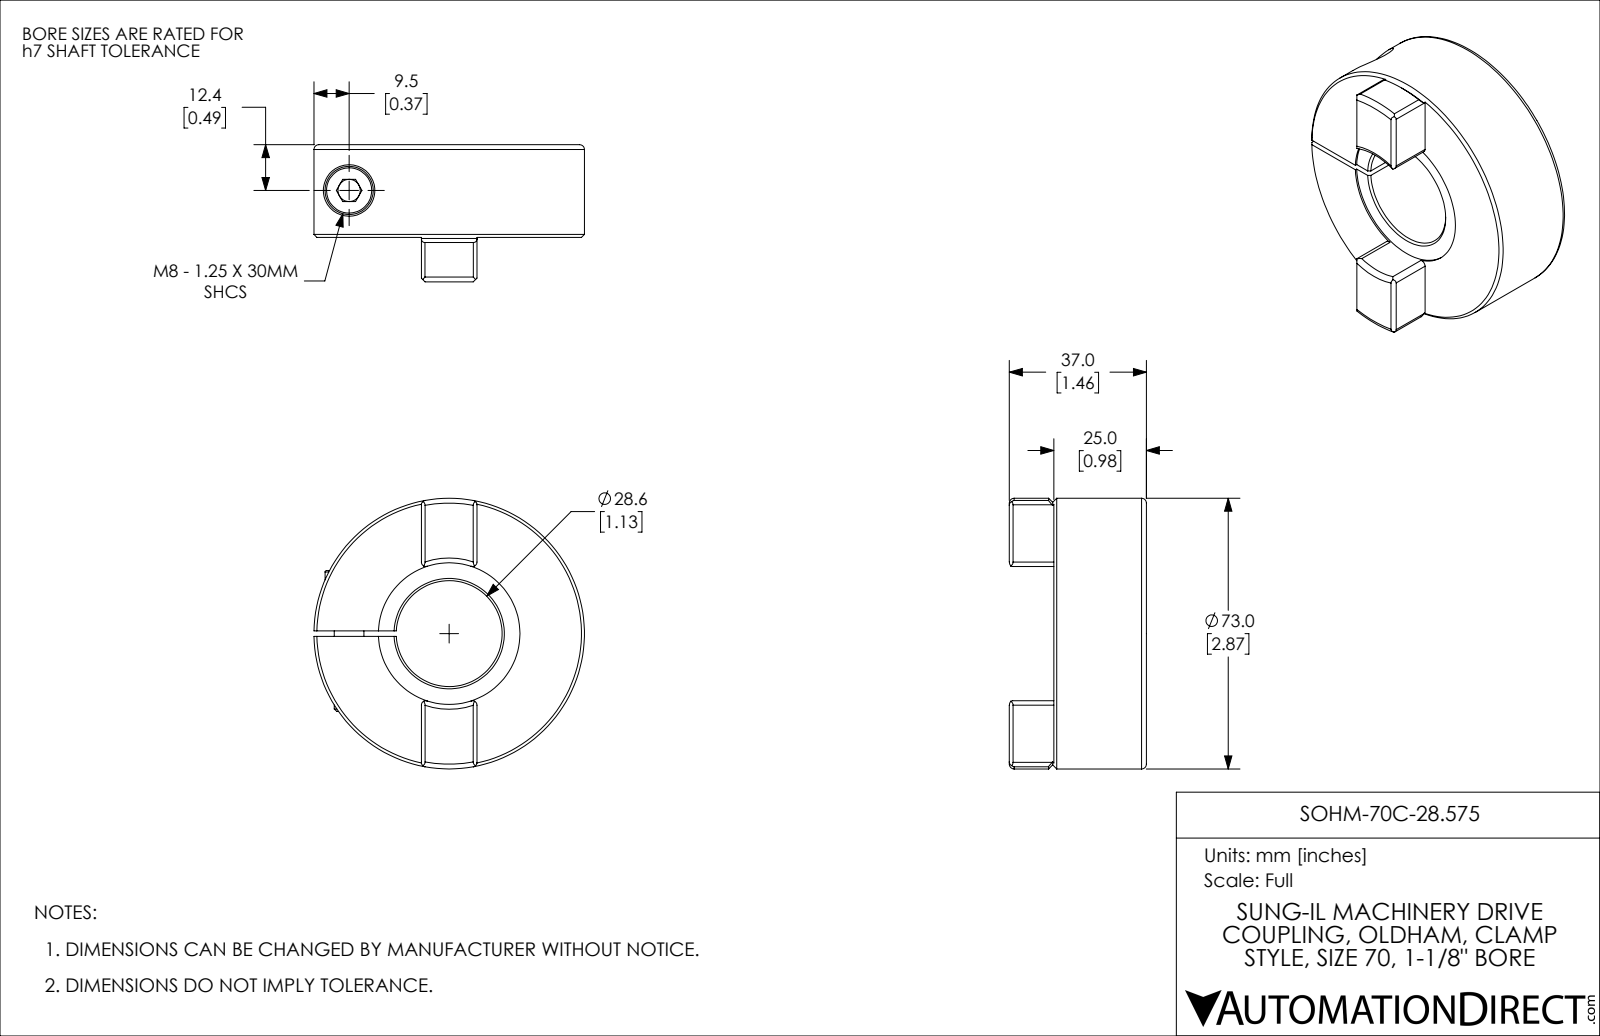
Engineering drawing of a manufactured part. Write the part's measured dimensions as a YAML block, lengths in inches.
part_name: "SOHM-70C-28.575"
step_written_by: "SolidWorks 2021 (CONFIG_CONTROL_DESIGN)"
units: inches
bodies: {solids: 2, faces: 94, planar: 35, cylindrical: 30, other: 29}
overall_size: [2.874, 2.874, 1.457]
volume: 5.63
surface_area: 30.74
round_holes:
  - {diameter: 0.236, count: 1}
  - {diameter: 0.268, count: 1}
  - {diameter: 0.335, count: 1}
  - {diameter: 0.547, count: 1}
  - {diameter: 1.125, count: 1}
  - {diameter: 1.504, count: 1}
round_bosses_or_shafts:
  - {diameter: 2.874, count: 1}
  - {diameter: 0.512, count: 1}
  - {diameter: 0.315, count: 1}
partial_cylinders:
  - {radius: 0.047, count: 8}
  - {radius: 1.969, count: 1}
face_to_face_distances: [0.984, 0.059, 0.965, 0.02, 1.457, 0.492, 0.472, 0.591, 0.384, 0.325]
